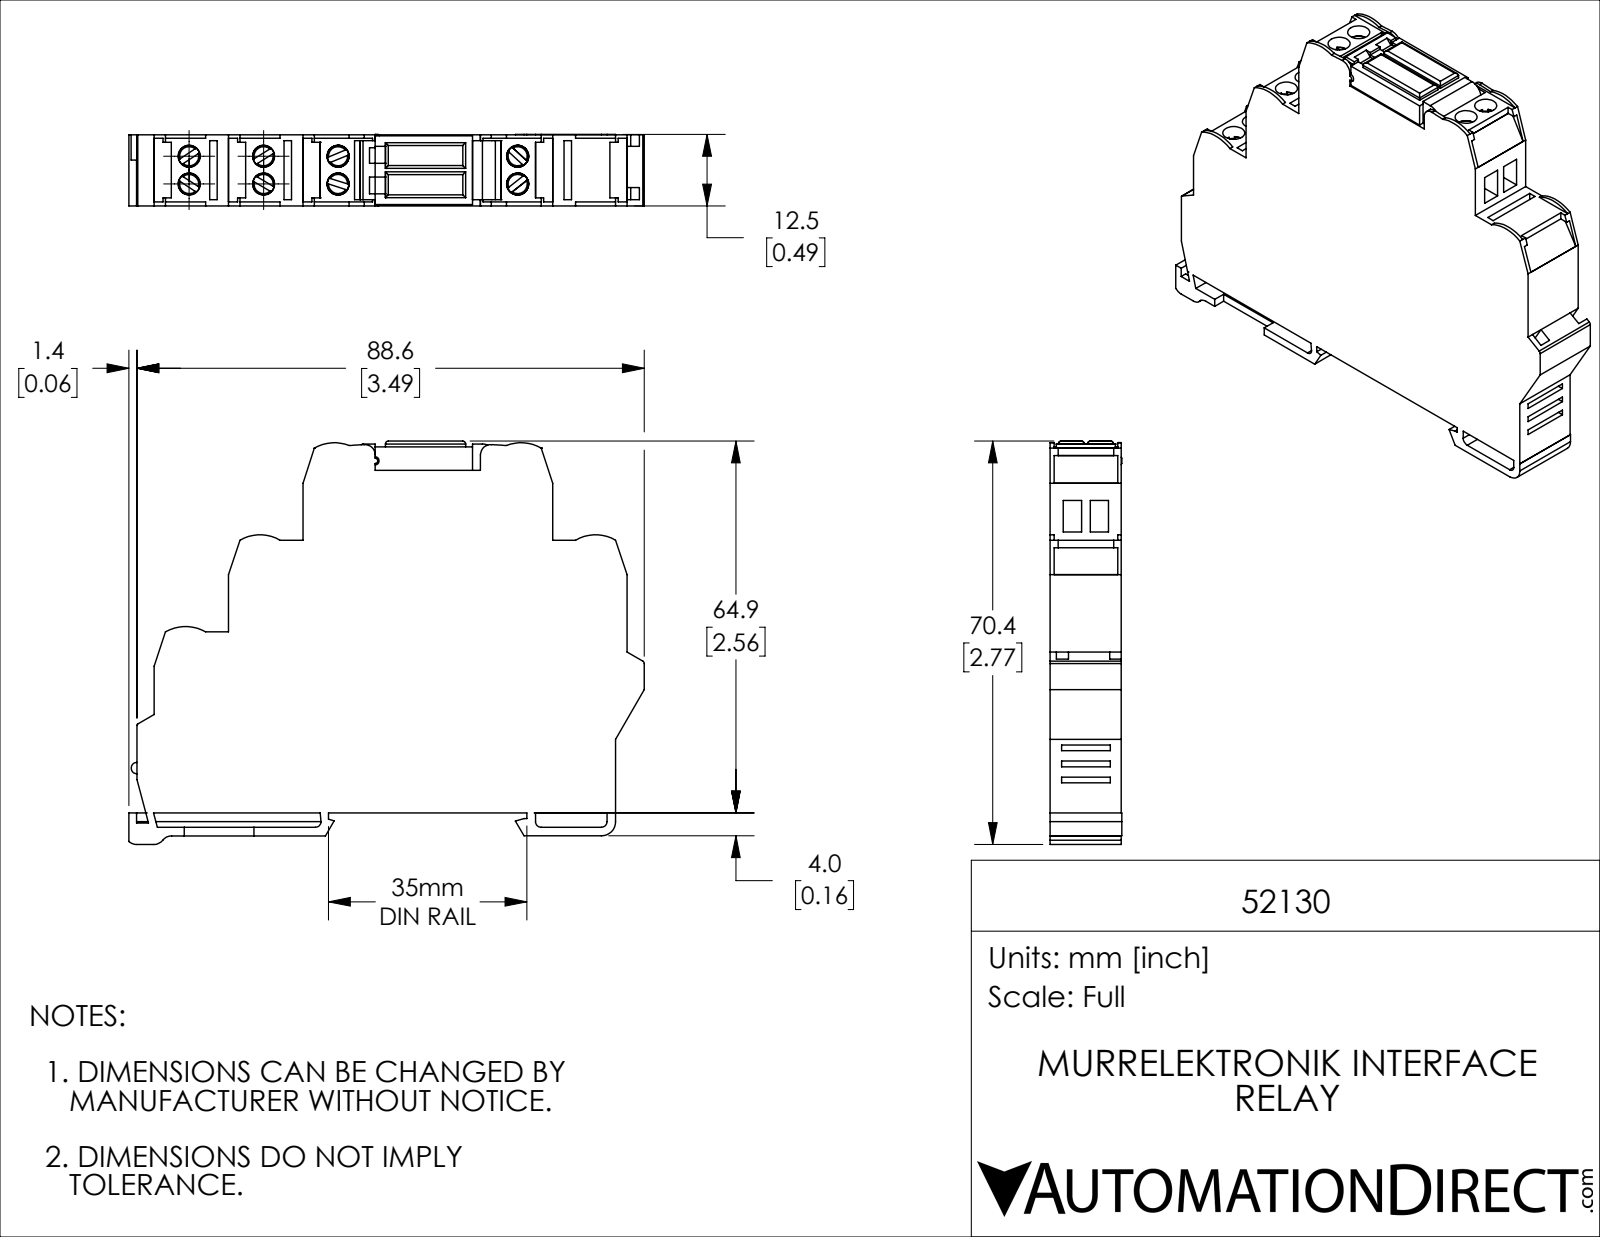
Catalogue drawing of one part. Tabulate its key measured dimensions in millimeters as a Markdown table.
| quantity | value |
| --- | --- |
| part name | 52130 |
| STEP written by | SolidWorks 2019 (CONFIG_CONTROL_DESIGN) |
| units | millimeters |
| bodies | 1 solid, 419 faces (315 planar, 78 cylindrical, 26 other) |
| overall size | 90 × 70.4 × 12.5 |
| volume | 53 980 mm³ |
| surface area | 17 490 mm² |
| round holes (diameter × count) | 3.9 × 8 |
| round bosses / shafts (diameter × count) | 3.8 × 8 |
| partial cylindrical surfaces (radius × count) | 0.5 × 9, 7 × 5, 1 × 4, 2 × 3, 0.7 × 2, 1.8 × 2, 2.3 × 2, 0.3 × 1 |
| main face-to-face distances | 12.4, 1.5, 4, 1, 2.5, 5.5, 4.7, 3.2, 5.3, 47.6 |
| hole center spacings | 13, 4.9, 13.9, 26, 26.4, 31.4, 31.7, 44.3 |
